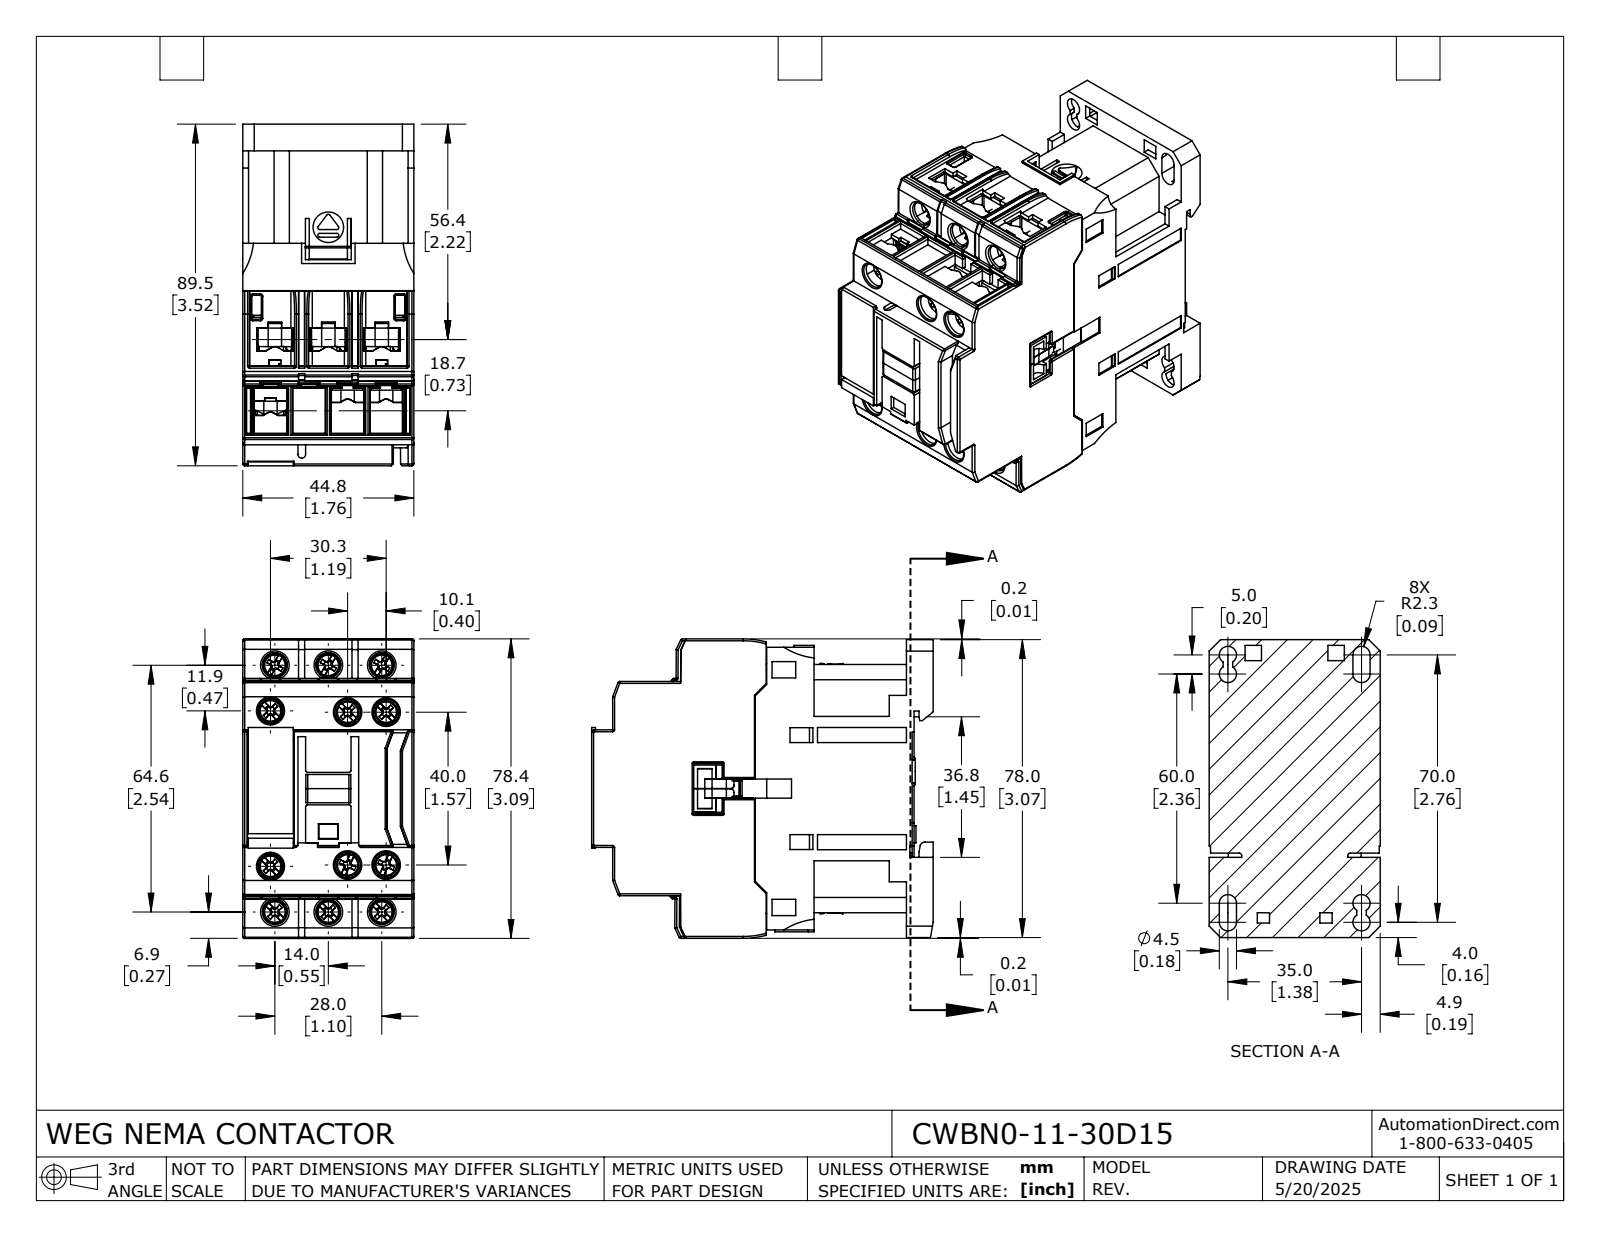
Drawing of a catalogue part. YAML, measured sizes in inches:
part_name: "CWBN0-11-30D15"
step_written_by: "SolidWorks 2024 (AUTOMOTIVE_DESIGN)"
units: inches
bodies: {solids: 44, faces: 3238, planar: 2285, cylindrical: 627, other: 326}
overall_size: [3.522, 3.087, 1.764]
volume: 13.37
surface_area: 117.1
round_holes:
  - {diameter: 0.124, count: 12}
  - {diameter: 0.256, count: 6}
  - {diameter: 0.177, count: 4}
round_bosses_or_shafts:
  - {diameter: 0.169, count: 12}
  - {diameter: 0.138, count: 12}
  - {diameter: 0.107, count: 7}
  - {diameter: 0.107, count: 5}
partial_cylinders:
  - {radius: 0.02, count: 127}
  - {radius: 0.012, count: 52}
  - {radius: 0.071, count: 24}
  - {radius: 0.964, count: 24}
  - {radius: 2.128, count: 24}
  - {radius: 0.016, count: 20}
  - {radius: 0.039, count: 19}
  - {radius: 0.106, count: 11}
face_to_face_distances: [1.764, 0.047, 1.717, 1.754, 0.022, 0.276, 1.776, 0.059, 0.024, 1.695]
hole_center_spacings: [0.551, 1.102, 2.602, 2.602, 2.543, 2.543, 0.197, 0.398]
